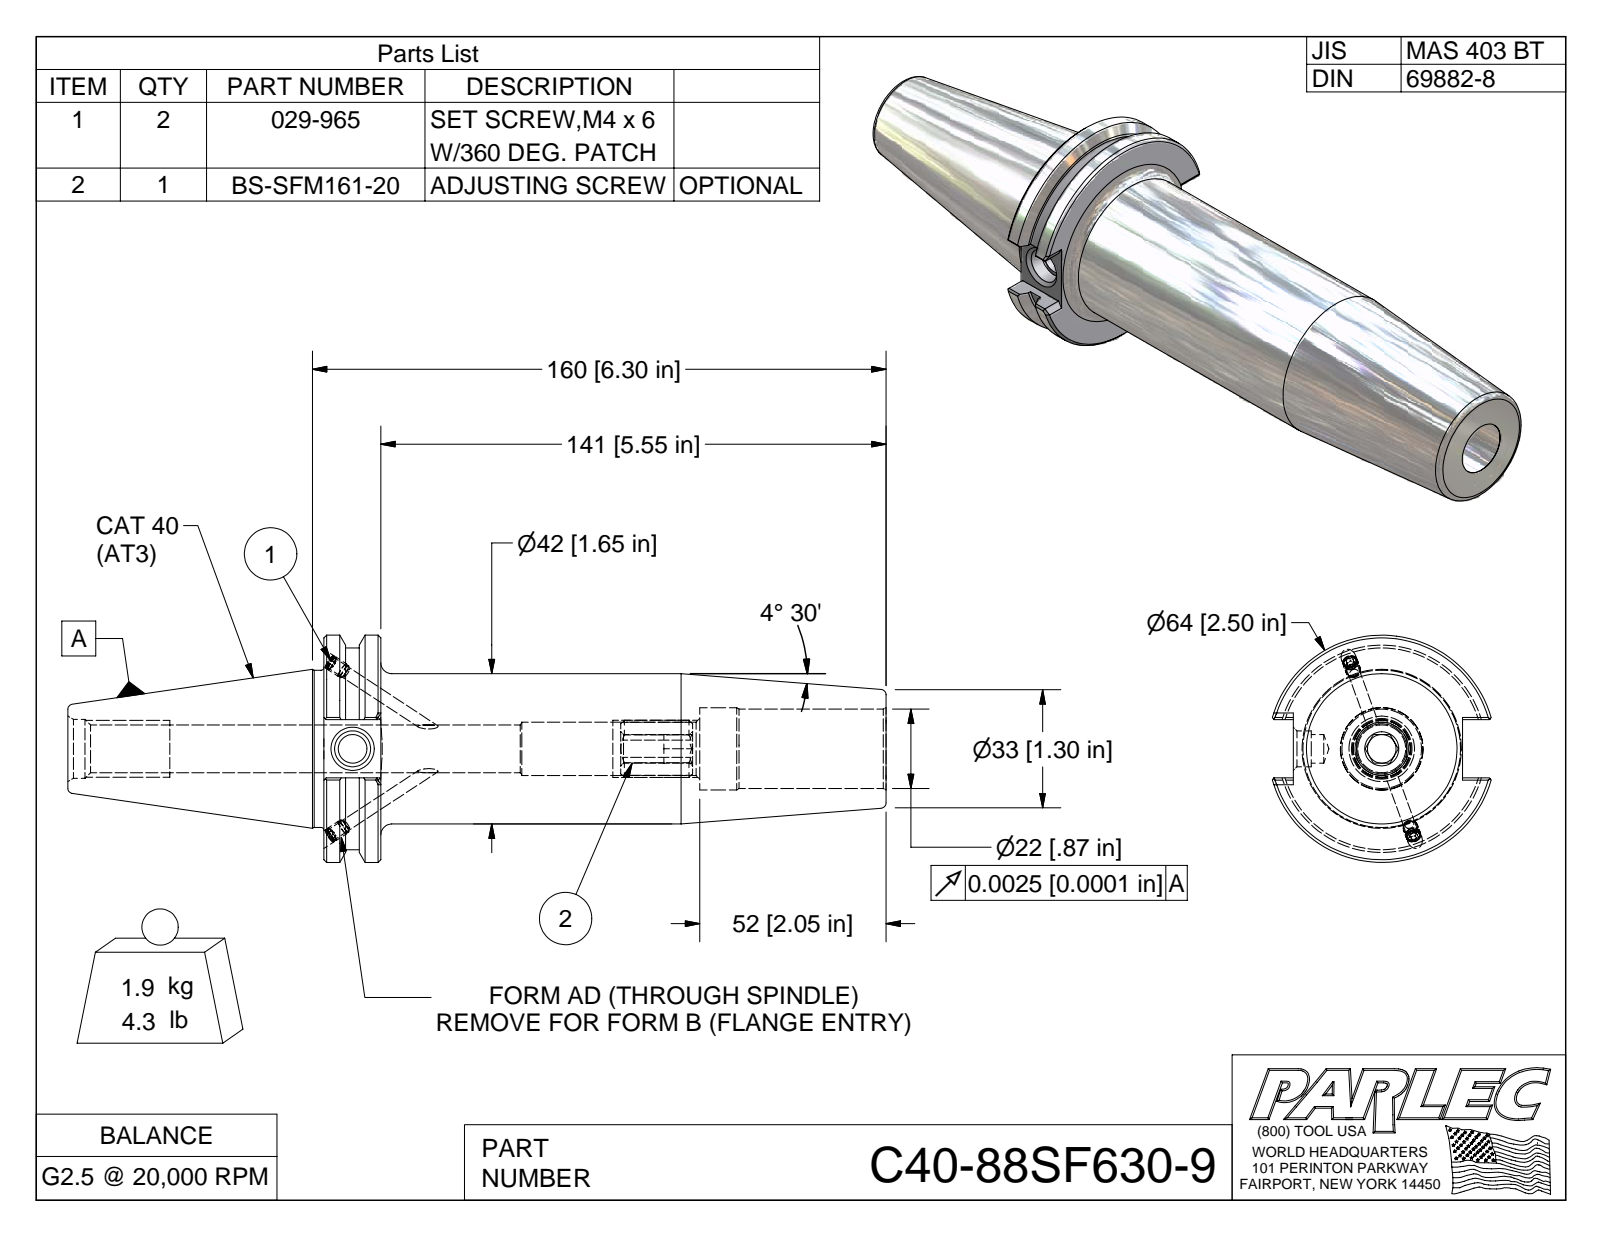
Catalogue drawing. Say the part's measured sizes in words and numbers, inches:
The part is named "C40-88SF630-9; C40BC-88SF630-9-1; 029-965; BS-SFM161-20". Its 3-D file was written by "Autodesk Inventor 2009 (AUTOMOTIVE_DESIGN)". It is 4 solids with 132 faces: 66 planar, 22 cylindrical and 44 other. Overall it measures 8.987 by 2.5 by 2.403 inches. Its volume is 15.11 cubic inches and its surface area 74.37 square inches. Round holes: 2 of diameter 0.13, 2 of diameter 0.161, 1 of diameter 0.874, 1 of diameter 0.904. Round bosses or shafts: 2 of diameter 0.165, 2 of diameter 0.157, 1 of diameter 2.5, 1 of diameter 2.219, 1 of diameter 1.73, 1 of diameter 1.654. Partial cylindrical surfaces (rounded edges, fillets, slot ends): 1 of radius 0.315. The main face-to-face distances are 0.625, 6.175, 5.55, 6.174, 5.549, 4.128, 3.502, 2.047, 2.047, 0.64.
